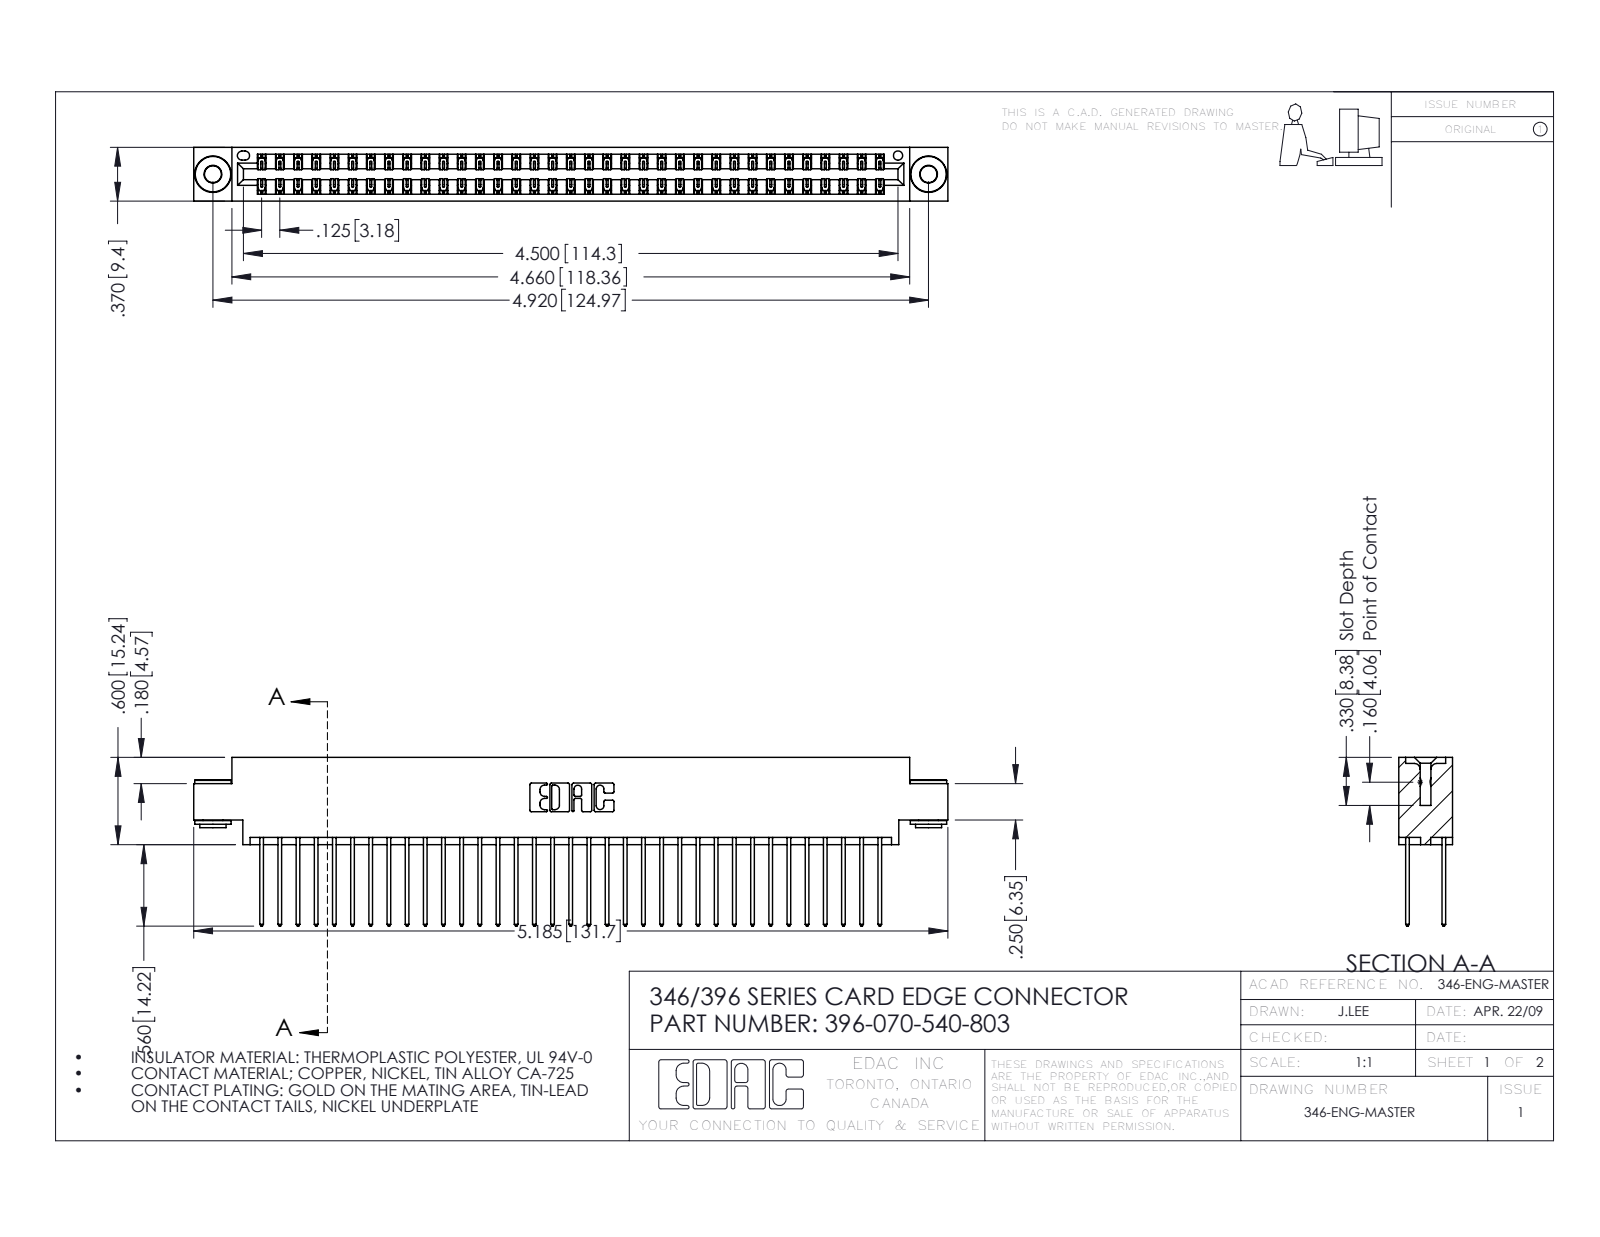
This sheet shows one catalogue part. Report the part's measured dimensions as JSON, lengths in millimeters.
{"part_name": "396-070-540-803; 345-292-001_345-293-140; 346 Part_0.170 Offset - 0.156 Dia-TH; 345-250-002_345-250-002-102", "step_written_by": "SolidWorks 2016 (CONFIG_CONTROL_DESIGN)", "units": "millimeters", "bodies": {"solids": 73, "faces": 3804, "planar": 2540, "cylindrical": 1256, "other": 8}, "overall_size": [131.7, 29.5, 9.4], "volume_mm3": 12900, "surface_area_mm2": 19300, "round_holes": [[2.9, 2], [4, 2], [1.6, 1]], "round_bosses_or_shafts": [[6.4, 2], [4.6, 2], [3.5, 2]], "partial_cylinders_radius": [[0.2, 105], [0.3, 70], [0.3, 22], [0.2, 6], [0.8, 6], [0.7, 3], [0.4, 2], [0.6, 2]], "face_to_face_distances": [1.2, 8.2, 6.4, 0.6, 9.4, 1.8, 7.6, 7, 3.8, 5.6], "hole_center_spacings": [6.2, 119.7, 125]}
